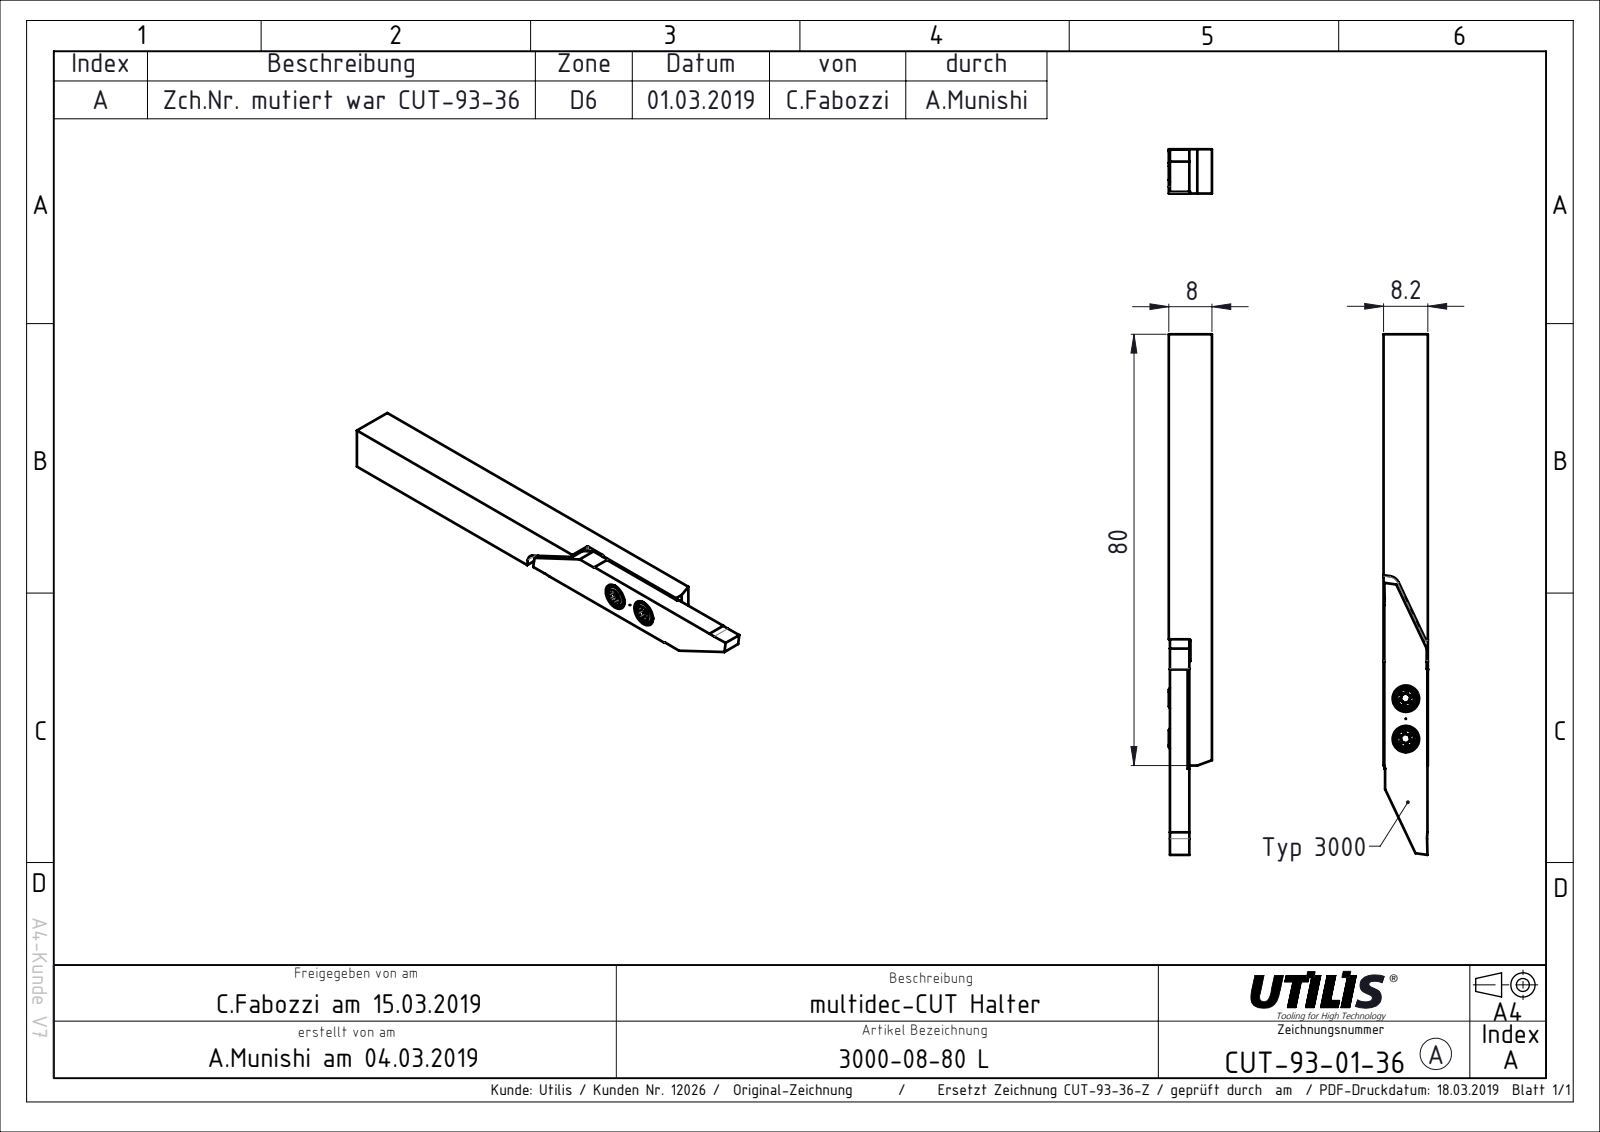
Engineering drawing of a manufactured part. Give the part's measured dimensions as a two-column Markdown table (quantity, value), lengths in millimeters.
| quantity | value |
| --- | --- |
| part name | CUT-93-36 |
| STEP written by | SolidWorks 2016 (AUTOMOTIVE_DESIGN) |
| units | millimeters |
| bodies | 1 solid, 44 faces (34 planar, 9 cylindrical, 1 other) |
| overall size | 96.5 × 8.2 × 8 |
| volume | 5 444 mm³ |
| surface area | 3 268 mm² |
| partial cylindrical surfaces (radius × count) | 0.2 × 4, 0.15 × 2, 10 × 2, 2.1 × 1 |
| main face-to-face distances | 8, 8.2, 7.8, 3.8, 3.6, 4.2, 4, 18.08, 18.56, 0.48 |
